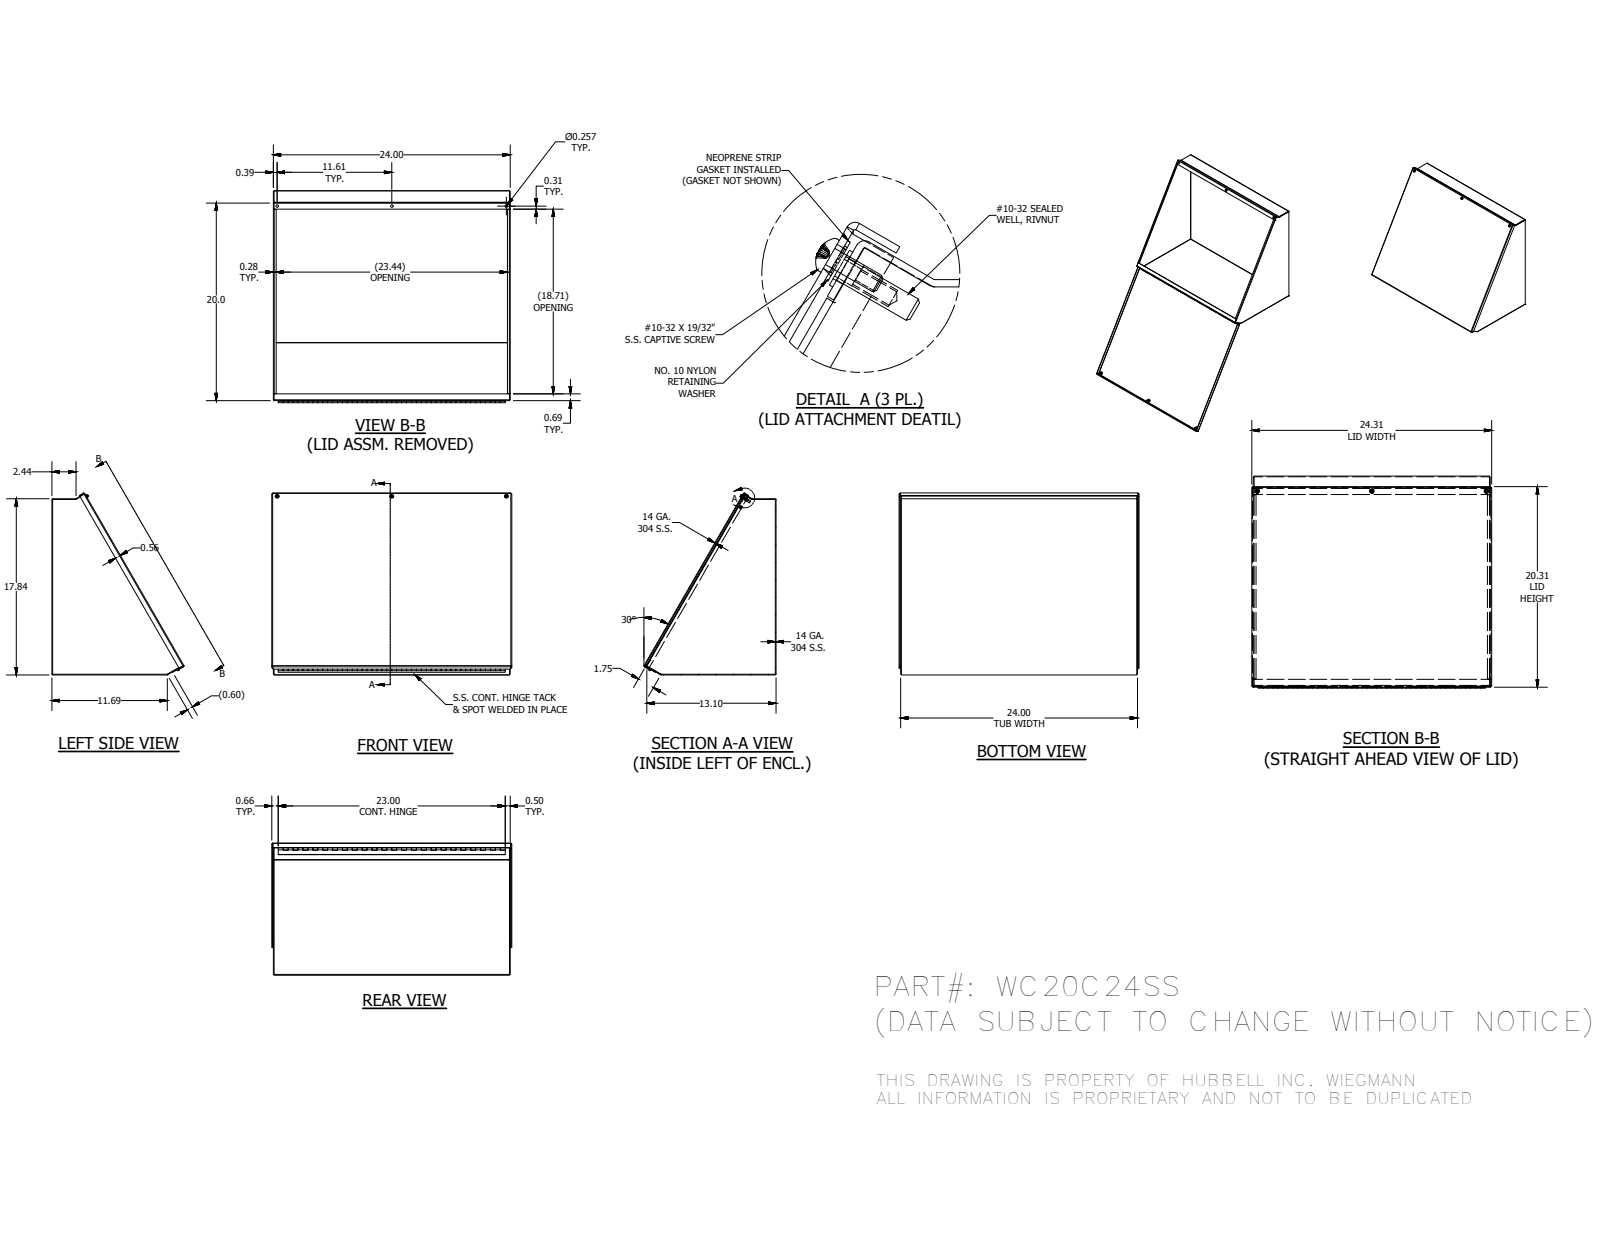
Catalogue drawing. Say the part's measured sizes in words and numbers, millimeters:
The part is named "WC20C24SSBTB; WC20C24SSLID; WC20CSSLS; WC20CSSRS (+8 more)". Its 3-D file was written by "Autodesk Inventor 2014 (AUTOMOTIVE_DESIGN)". It is 16 solids with 597 faces: 364 planar, 159 cylindrical and 74 other. Overall it measures 617.54 by 467.99 by 340.03 millimeters. Its volume is 2 077 000 cubic millimeters and its surface area 2 251 000 square millimeters. Round holes: 3 of diameter 3.96, 3 of diameter 4.98, 3 of diameter 6.53, 3 of diameter 7.06, 3 of diameter 7.14, 1 of diameter 2.96. Round bosses or shafts: 3 of diameter 11.51, 3 of diameter 10.31, 3 of diameter 9.47, 3 of diameter 6.3, 3 of diameter 4.83, 1 of diameter 5.08, 1 of diameter 2.54. Partial cylindrical surfaces (rounded edges, fillets, slot ends): 12 of radius 0.4, 12 of radius 2.28, 3 of radius 2.27. The main face-to-face distances are 1.88, 607.72, 605.84, 609.6, 451.35, 449.47, 453.23, 2.94, 3.97, 611.69. The hole center spacings are 294.97, 589.94, 1.31.
